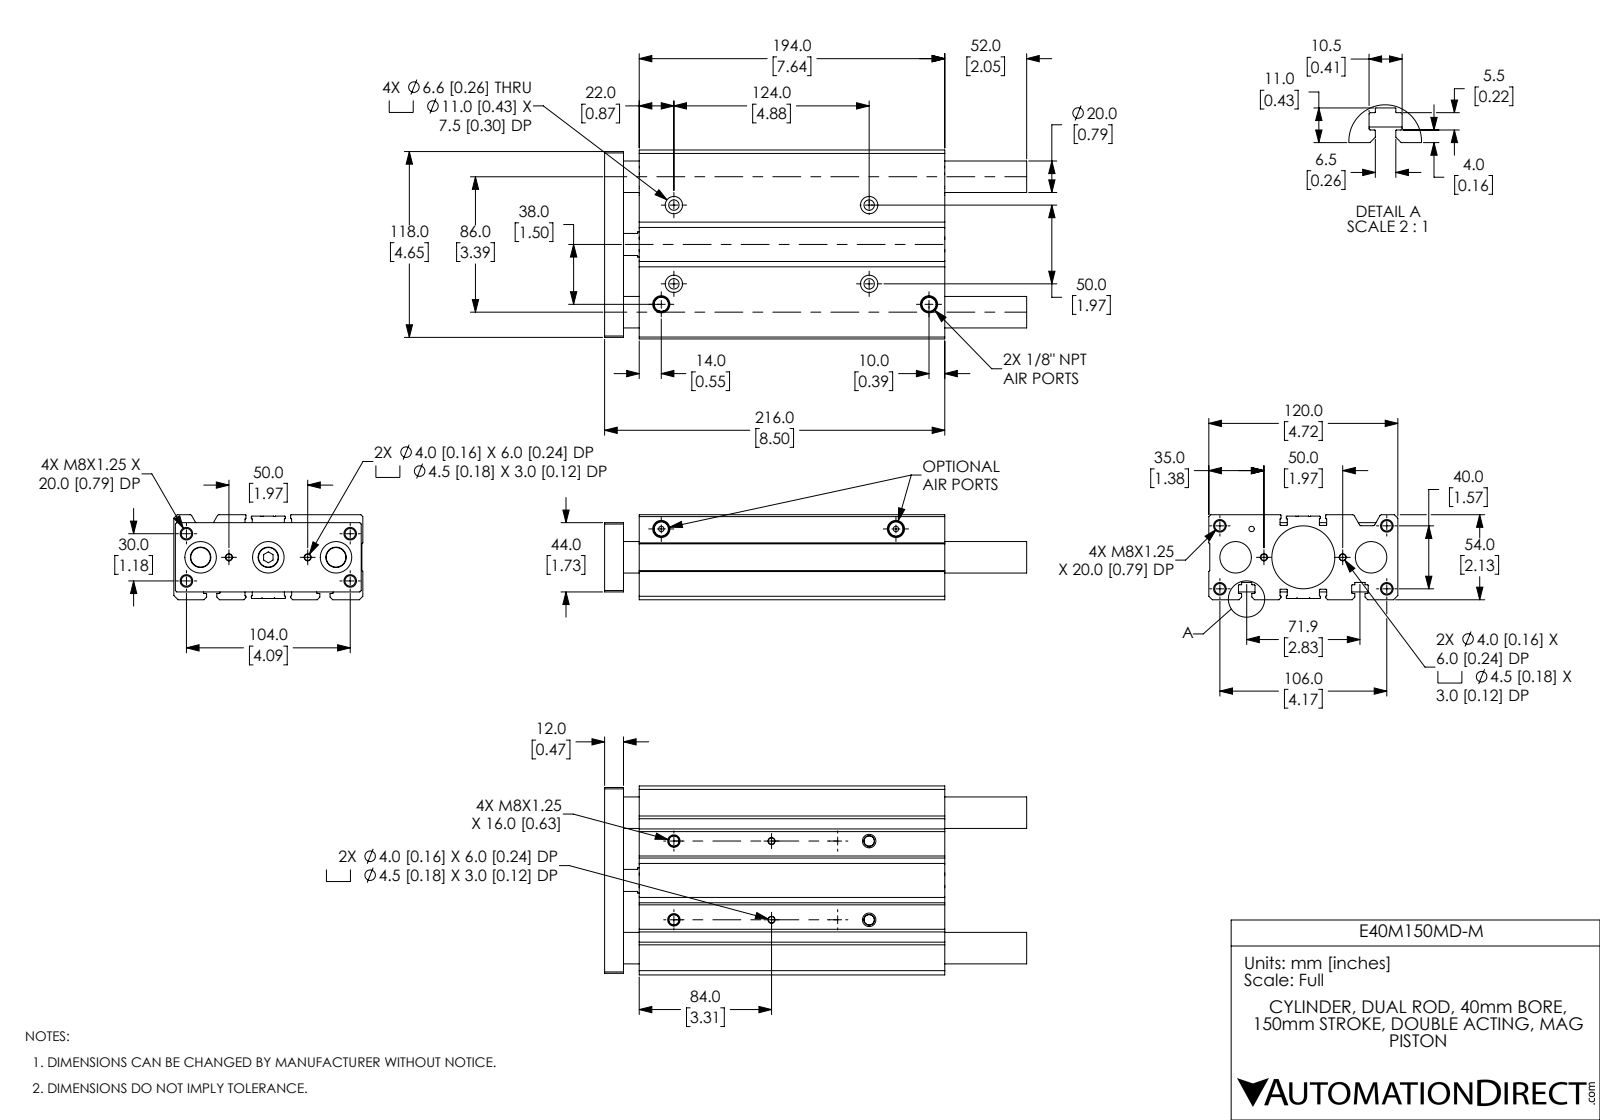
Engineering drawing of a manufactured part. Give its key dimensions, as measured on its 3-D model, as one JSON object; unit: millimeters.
{"part_name": "E40M150MD-M; E40M150MD-M_BODY; E40M150MD-M_ENDPLATE", "step_written_by": "SolidWorks 2019 (CONFIG_CONTROL_DESIGN)", "units": "millimeters", "bodies": {"solids": 5, "faces": 427, "planar": 139, "cylindrical": 194, "other": 94}, "overall_size": [268, 120, 54], "volume_mm3": 1091000, "surface_area_mm2": 224810, "round_holes": [[6.65, 10], [4, 4], [4.5, 4], [6.6, 4], [11, 4], [3.43, 3], [10, 3], [20, 3], [6.65, 2], [10.91, 2], [12.95, 2], [20, 1]], "round_bosses_or_shafts": [[16, 1], [12.95, 1]], "partial_cylinders_radius": [[0.2, 32], [0.4, 28], [1.2, 4], [0.3, 2]], "face_to_face_distances": [54, 120, 0.6, 22, 25, 12, 10, 216, 204, 194], "hole_center_spacings": [5.1, 17.49, 22.36, 30.89, 34.41, 35.01, 50, 54.12]}
